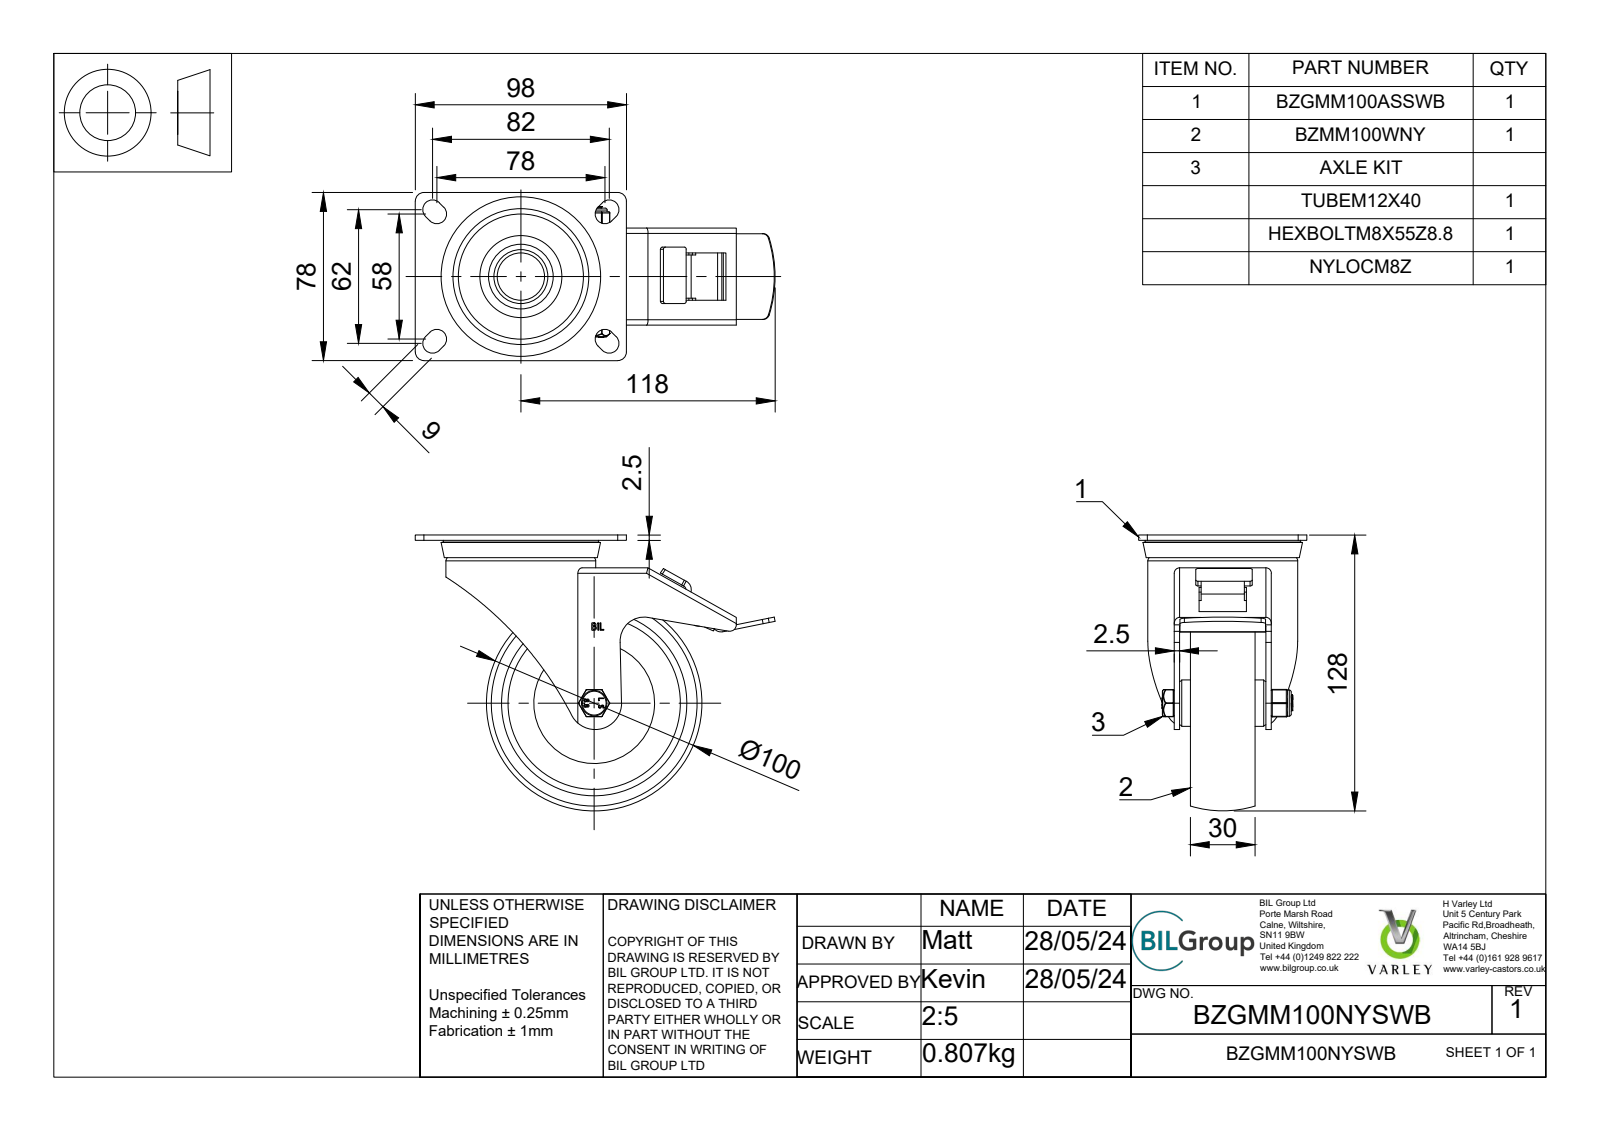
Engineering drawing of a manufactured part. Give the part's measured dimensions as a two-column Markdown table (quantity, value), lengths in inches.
| quantity | value |
| --- | --- |
| part name | BZGMM100NYSWB v3; BZGMM100ASSWB - 2 v1; ZINC PLATED, PRESSED STEEL FORKS; BRAKE PAD (+7 more) |
| STEP written by | Autodesk Translation Framework v13.14.0.145 (AUTOMOTIVE_DESIGN) |
| units | inches |
| bodies | 38 solids, 467 faces (188 planar, 161 cylindrical, 118 other) |
| overall size | 6.575 × 5.039 × 3.071 |
| volume | 11.51 in³ |
| surface area | 172.9 in² |
| round holes (diameter × count) | 0.026 × 2, 0.315 × 1, 0.323 × 1, 0.331 × 1, 0.339 × 1, 0.488 × 1, 1.024 × 1, 1.181 × 1, 2.539 × 1, 3.386 × 1 |
| round bosses / shafts (diameter × count) | 2.736 × 1, 1.85 × 1, 0.984 × 1, 0.846 × 1, 0.476 × 1, 0.469 × 1, 0.453 × 1, 0.31 × 1 |
| partial cylindrical surfaces (radius × count) | 0.02 × 18, 0.01 × 12, 0.049 × 8, 0.177 × 8, 0.157 × 5, 0.013 × 4, 0.025 × 4, 0.039 × 4 |
| main face-to-face distances | 0.098, 0.295, 0.866, 0.709, 0.807, 0.965, 1.673, 0.157, 0.118, 0.512 |
| hole center spacings | 0.127, 0.098 |
